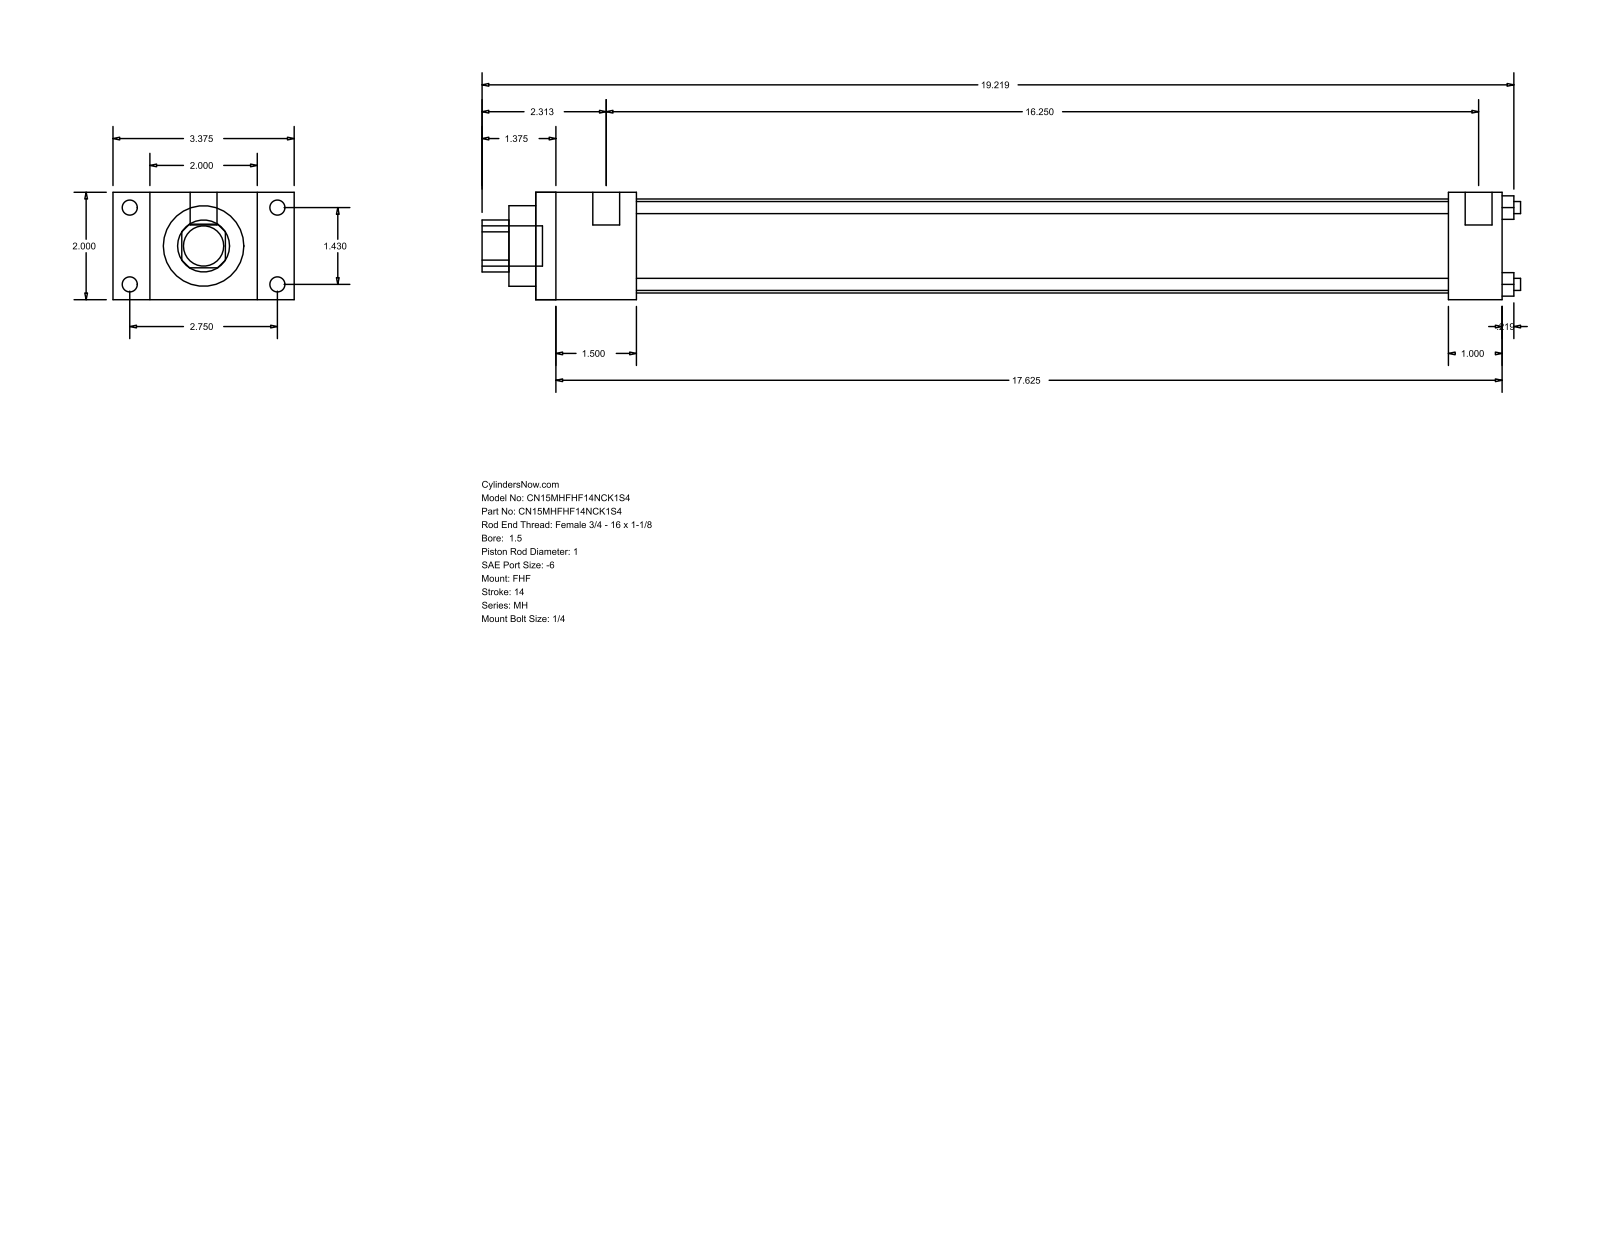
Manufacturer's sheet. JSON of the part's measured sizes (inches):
{"part_name": "MH_FHF__0150_1", "step_written_by": "GSSL Pune (CONFIG_CONTROL_DESIGN)", "units": "inches", "bodies": {"solids": 0, "faces": 88, "planar": 60, "cylindrical": 28, "other": 0}, "overall_size": [19.344, 3.375, 2], "round_holes": [[0.225, 4], [1, 1], [1.5, 1], [1.75, 1]], "round_bosses_or_shafts": [[0.281, 4], [0.219, 4], [0.5, 2], [0.75, 1]], "partial_cylinders_radius": [[0.484, 1]], "face_to_face_distances": [2, 0.687, 2.687, 1.875, 3.375, 18, 16.125, 1, 17, 15.125], "hole_center_spacings": [1.011, 1.43, 2.022]}
